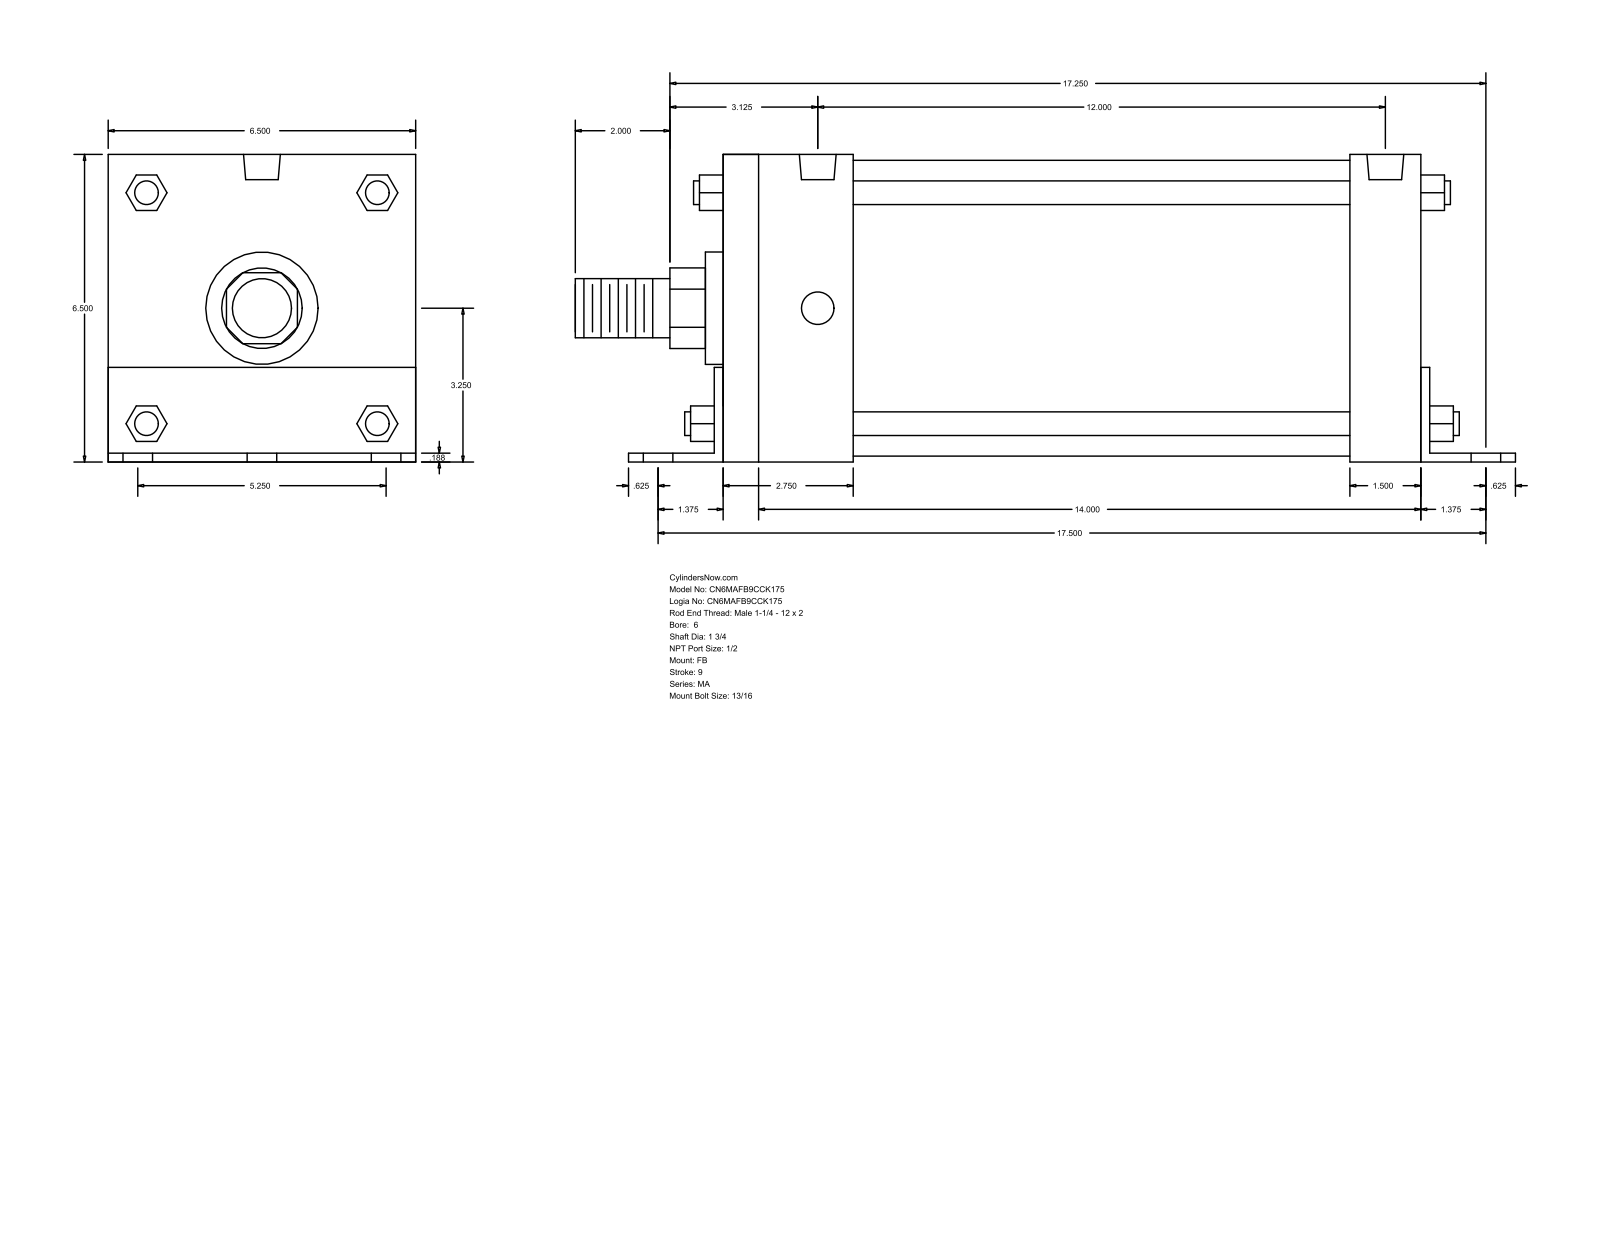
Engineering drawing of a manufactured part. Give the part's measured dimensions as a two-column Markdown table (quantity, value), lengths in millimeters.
| quantity | value |
| --- | --- |
| part name | MA_FB__0600_1.75 |
| STEP written by | GSSL Pune (CONFIG_CONTROL_DESIGN) |
| units | millimeters |
| bodies | 0 solids, 140 faces (105 planar, 35 cylindrical, 0 other) |
| overall size | 504.82 × 165.15 × 165.1 |
| round holes (diameter × count) | 20.64 × 6, 17.46 × 4, 19.77 × 2 |
| round bosses / shafts (diameter × count) | 12.7 × 4, 158.75 × 1, 60.33 × 1, 44.45 × 1, 31.75 × 1 |
| partial cylindrical surfaces (radius × count) | 21.63 × 1, 32.05 × 1 |
| main face-to-face distances | 165.1, 4.76, 374.66, 165.15, 379.42, 4.71, 160.39, 384.18, 69.85, 74.61 |
| hole center spacings | 66.67, 449.47, 444.5, 85.78, 108.6, 133.34, 304.8, 364.91 |
